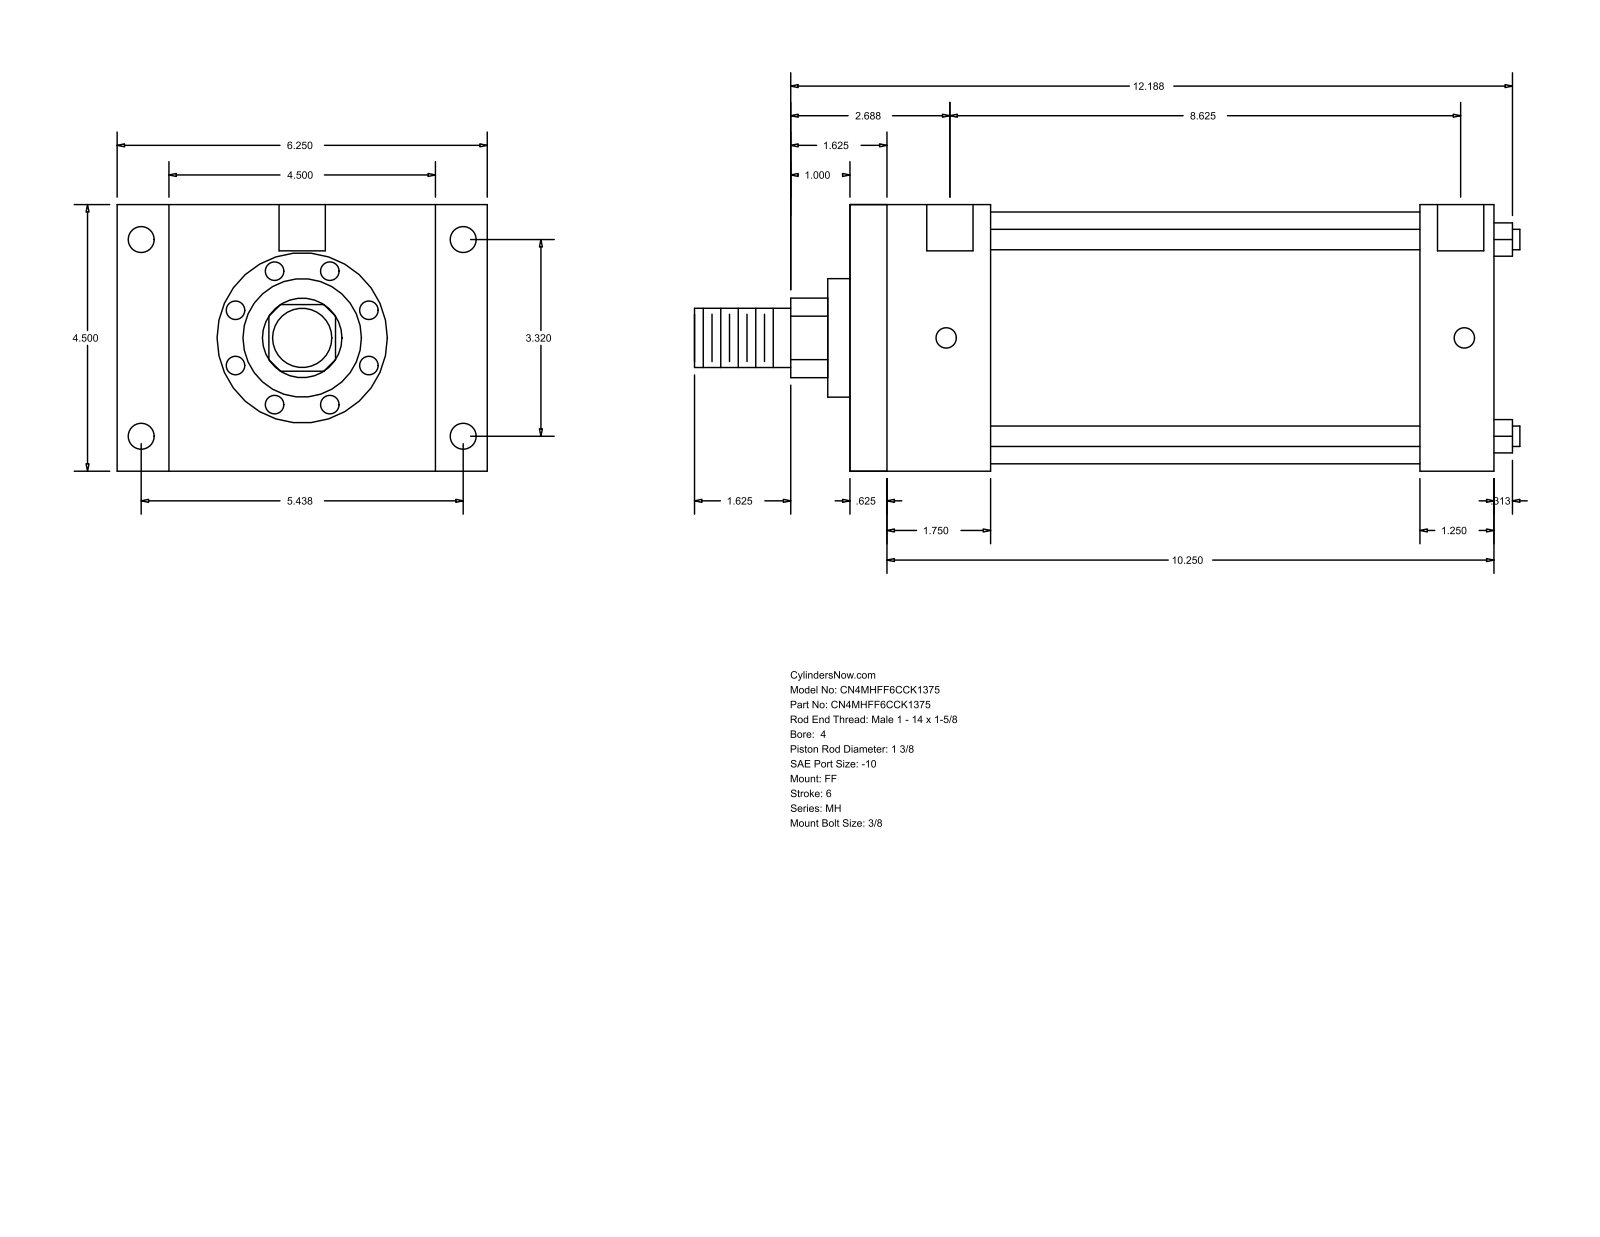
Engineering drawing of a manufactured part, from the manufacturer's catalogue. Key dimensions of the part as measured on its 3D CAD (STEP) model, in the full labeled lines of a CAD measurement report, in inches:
Part name (STEP PRODUCT): MH_FF__0400_1.375
STEP written by: GSSL Pune (CONFIG_CONTROL_DESIGN)
Units: inches
Bodies: 0 solids, 92 faces (64 planar, 28 cylindrical, 0 other)
Overall size (bounding box): 13.937 × 6.25 × 4.5
Round holes (diameter × count): ⌀0.344 ×4, ⌀0.438 ×4, ⌀0.781 ×2
Round bosses / shafts (diameter × count): ⌀0.345 ×4, ⌀4.25 ×1, ⌀2 ×1, ⌀1.375 ×1, ⌀1 ×1
Partial cylindrical surfaces — rounded edges, fillets, slot ends (radius × count): R0.672 ×1
Main face-to-face distances: 4.5, 10.875, 0.625, 10.25, 2.375, 1.75, 8.5, 9.625, 9, 7.25
Hole centre spacings: 0.063, 3.32, 5.438, 6.371, 8.688, 8.75, 8.625
